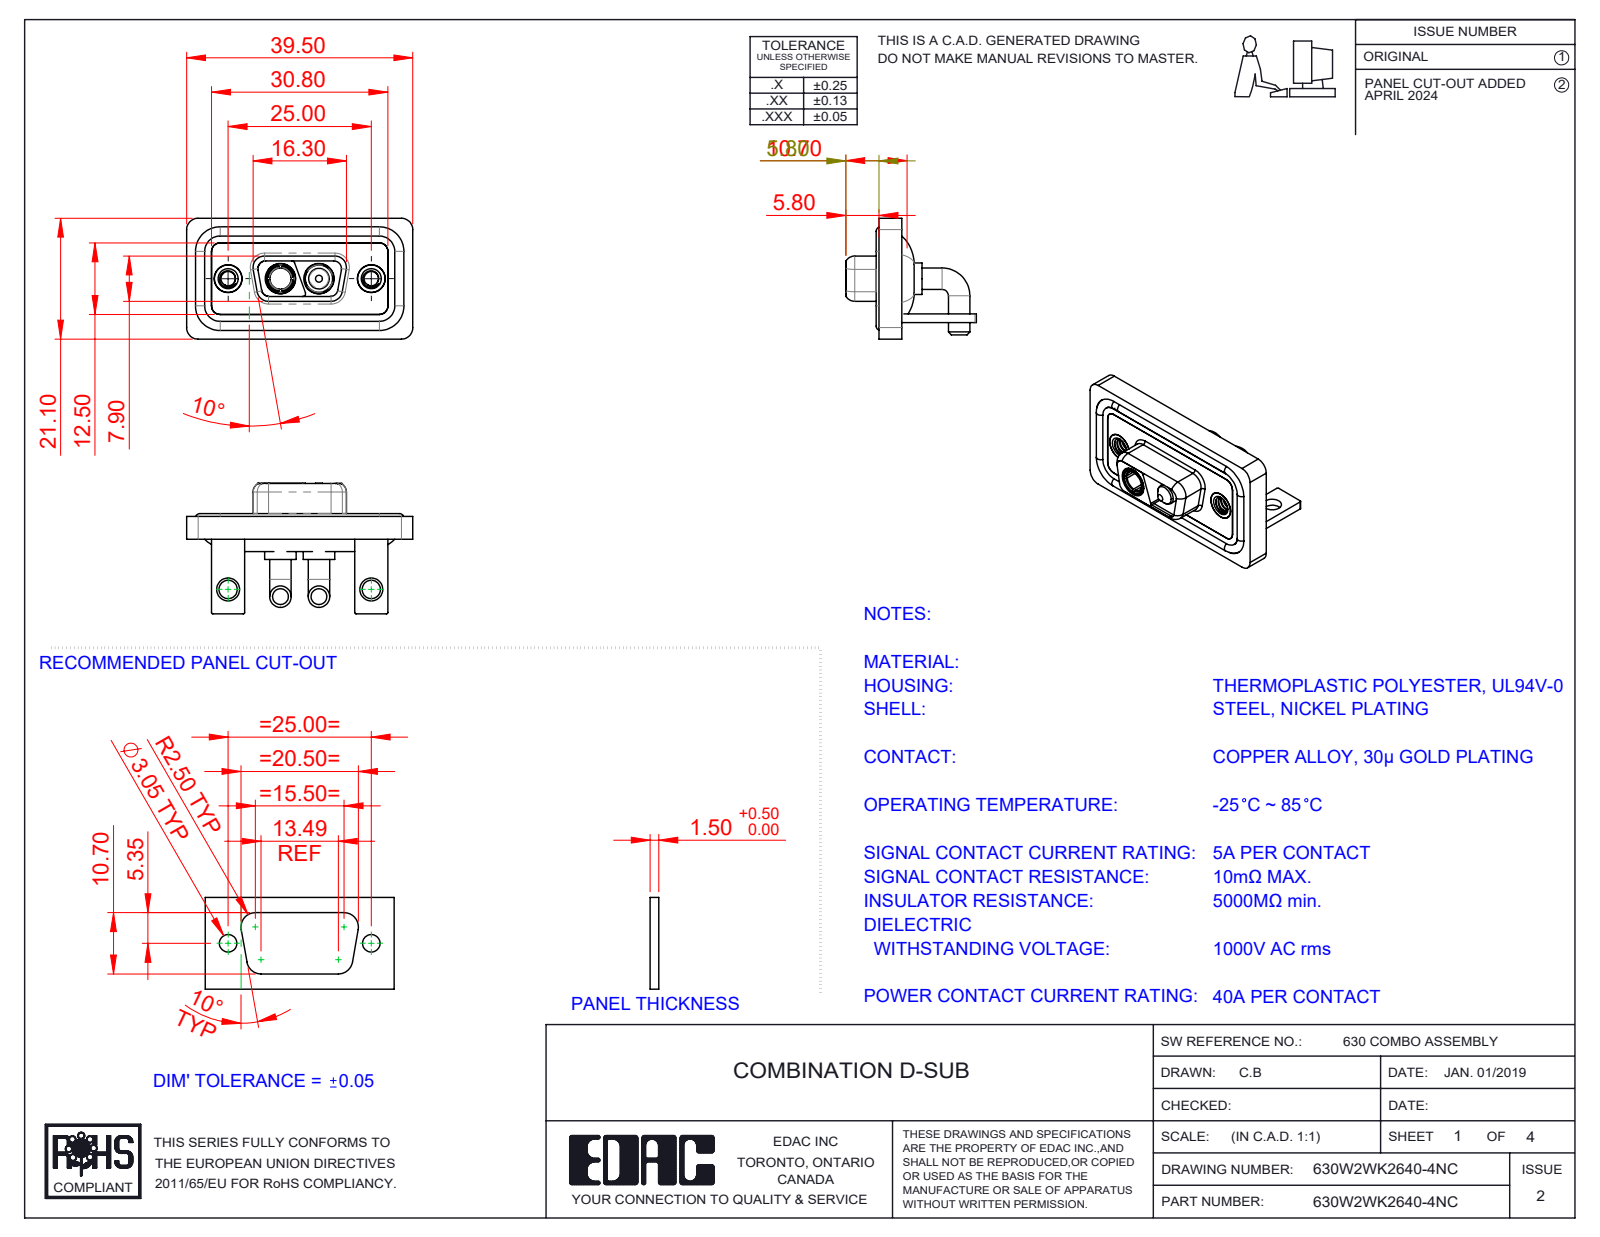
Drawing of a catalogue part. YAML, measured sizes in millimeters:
part_name: "Power Socket_40A RA; 630Combo Shell Rear_09 Contacts; Power Pin_40A RA; 630Combo Threaded Rivet_A (+5 more)"
step_written_by: "SolidWorks 2023 (CONFIG_CONTROL_DESIGN)"
units: millimeters
bodies: {solids: 13, faces: 550, planar: 164, cylindrical: 257, other: 129}
overall_size: [39.5, 22.8, 21.1]
volume: 5212
surface_area: 8320
round_holes:
  - {diameter: 4.85, count: 4}
  - {diameter: 2.5, count: 2}
  - {diameter: 3.2, count: 2}
  - {diameter: 4, count: 2}
  - {diameter: 4.05, count: 2}
  - {diameter: 5, count: 2}
  - {diameter: 5.3, count: 2}
  - {diameter: 3.7, count: 1}
round_bosses_or_shafts:
  - {diameter: 3.75, count: 4}
  - {diameter: 1.6, count: 4}
  - {diameter: 5.5, count: 2}
  - {diameter: 5.2, count: 2}
  - {diameter: 4.95, count: 2}
  - {diameter: 4.8, count: 2}
  - {diameter: 4.75, count: 2}
  - {diameter: 4.96, count: 1}
partial_cylinders:
  - {radius: 2, count: 19}
  - {radius: 1.5, count: 18}
  - {radius: 0.25, count: 16}
  - {radius: 1.35, count: 8}
  - {radius: 1.6, count: 8}
  - {radius: 0.5, count: 7}
  - {radius: 0.6, count: 4}
  - {radius: 0.65, count: 4}
face_to_face_distances: [0.4, 2.9, 1.5, 1.1, 3.7, 1.8, 0.8, 2.5, 1.6, 3.1]
hole_center_spacings: [9.14, 15.86, 25, 6.72]
